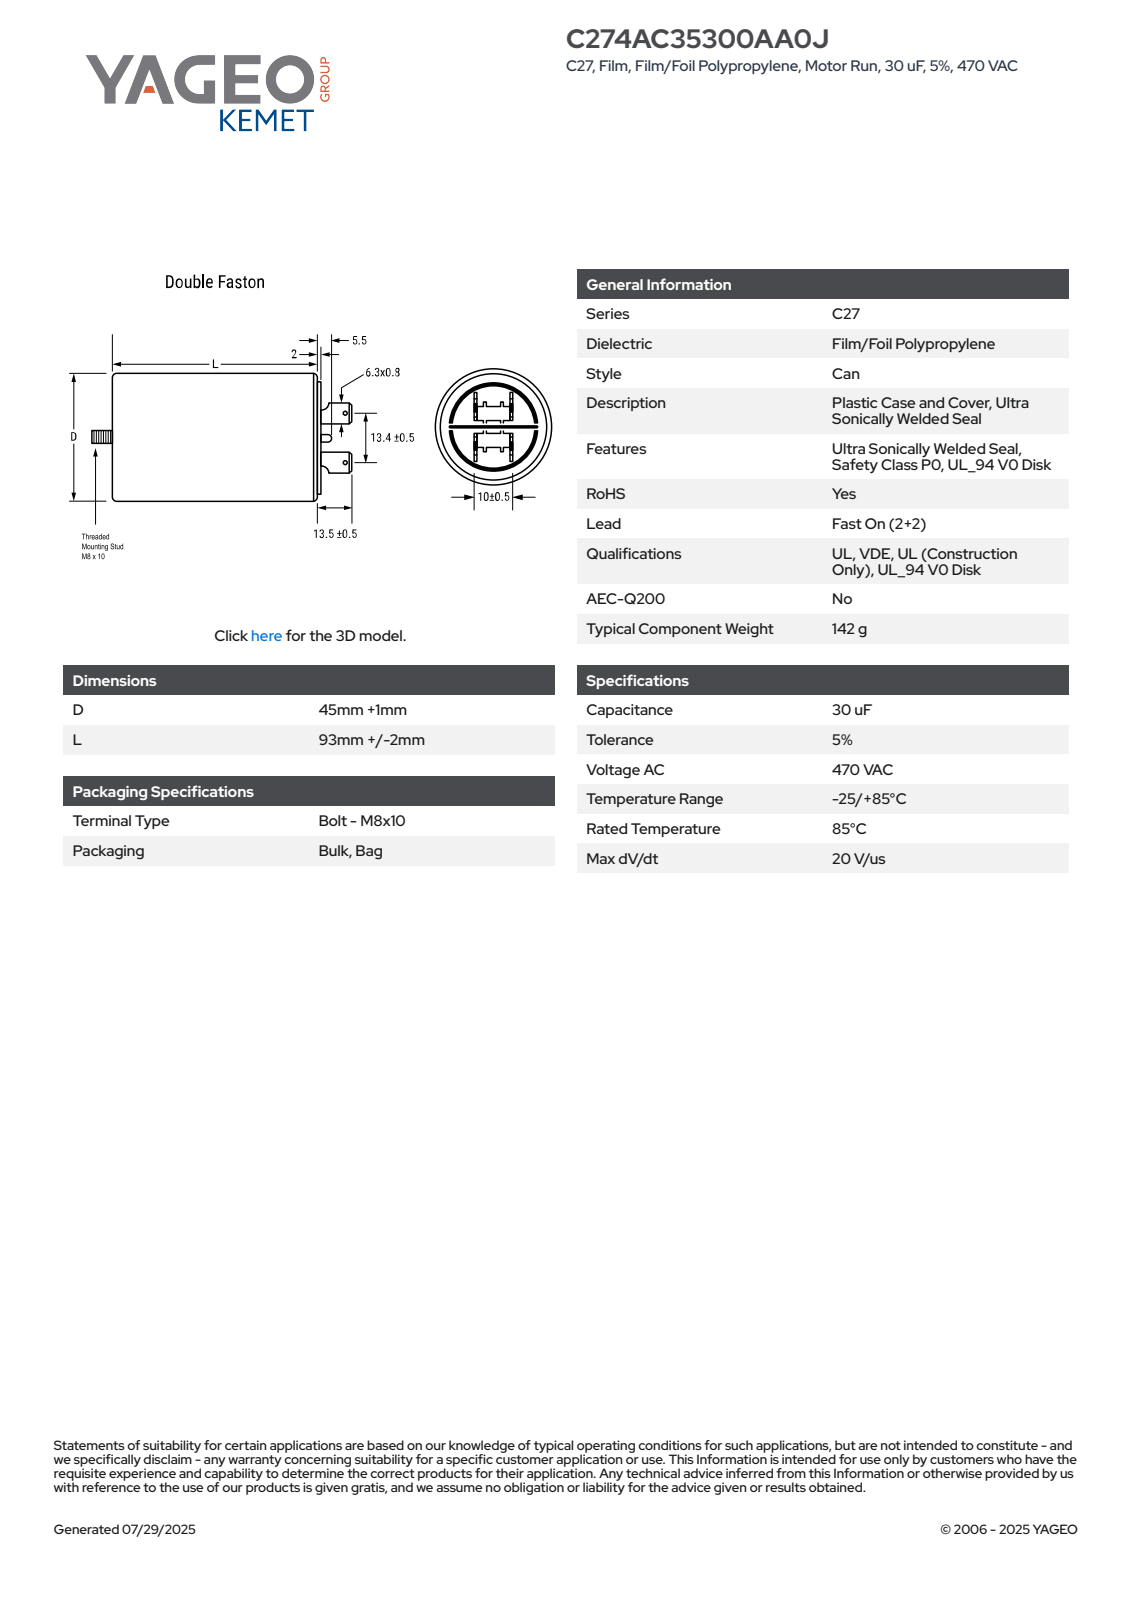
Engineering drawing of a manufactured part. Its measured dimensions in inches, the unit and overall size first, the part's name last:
Units: inches
Overall size (bounding box): 4.685 × 1.811 × 1.811
Round holes (diameter × count): ⌀0.047 ×2
Round bosses / shafts (diameter × count): ⌀1.811 ×1, ⌀1.393 ×1, ⌀0.315 ×1
Partial cylindrical surfaces — rounded edges, fillets, slot ends (radius × count): R0.01 ×9, R0.157 ×2, R0.905 ×1
Main face-to-face distances: 3.819, 3.74, 0.079, 0.031, 0.382, 0.413, 0.35, 0.02, 0.394, 4.134
Hole centre spacings: 0.547
Volume: 9.788 in³ · Surface area: 28.17 in²
Bodies: 1 solid, 137 faces (49 planar, 53 cylindrical, 35 other)
Part name (STEP PRODUCT): CFM_C27DF_45X93_D46L95
STEP written by: SolidWorks 2014 (AUTOMOTIVE_DESIGN)
